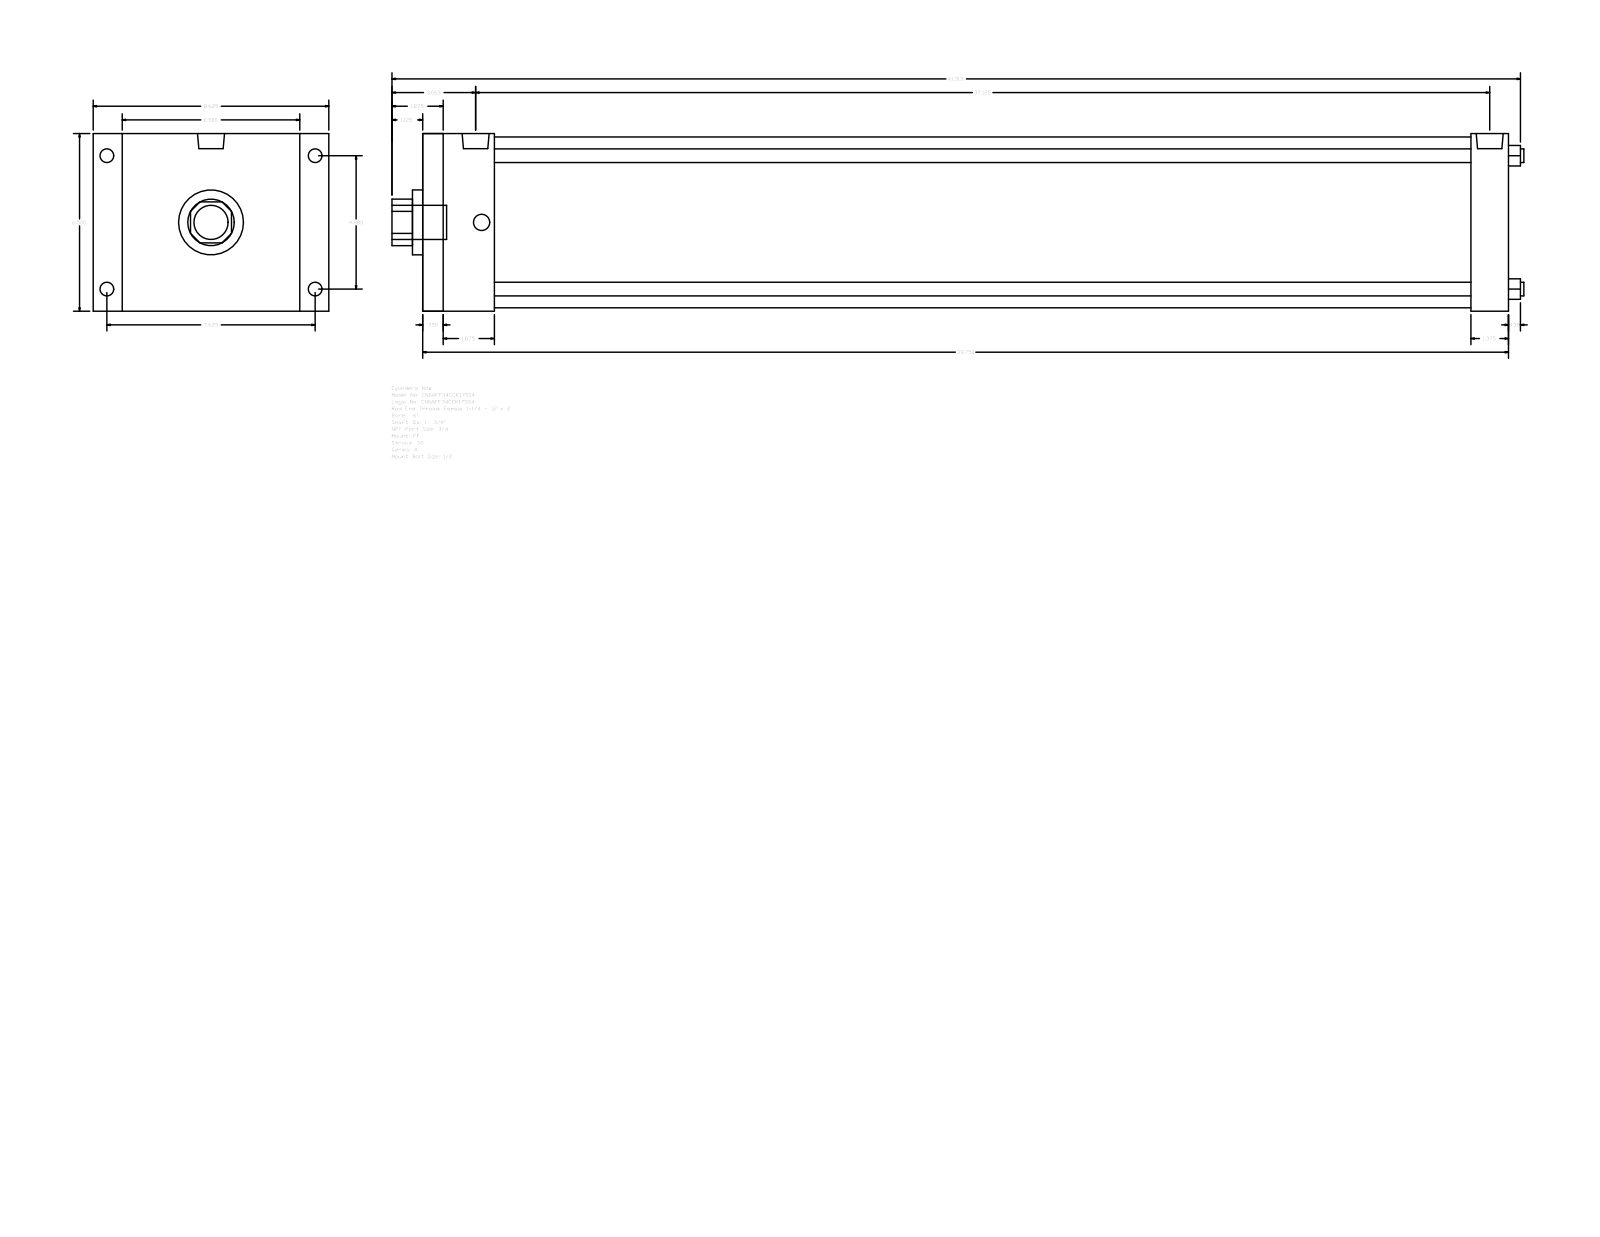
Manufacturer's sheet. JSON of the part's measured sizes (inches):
{"part_name": "A_FF__0600_1.75", "step_written_by": "GSSL Pune (CONFIG_CONTROL_DESIGN)", "units": "inches", "bodies": {"solids": 0, "faces": 92, "planar": 64, "cylindrical": 28, "other": 0}, "overall_size": [41.437, 8.625, 6.5], "round_holes": [[0.5, 4], [1.75, 1], [2.375, 1], [6.25, 1]], "round_bosses_or_shafts": [[0.594, 4], [0.5, 4], [0.989, 2], [1.25, 1]], "partial_cylinders_radius": [[0.852, 1]], "face_to_face_distances": [6.5, 39.75, 0.75, 39, 1.375, 2.625, 1.875, 37.125, 38.375, 37.625], "hole_center_spacings": [3.451, 4.88, 6.902]}
